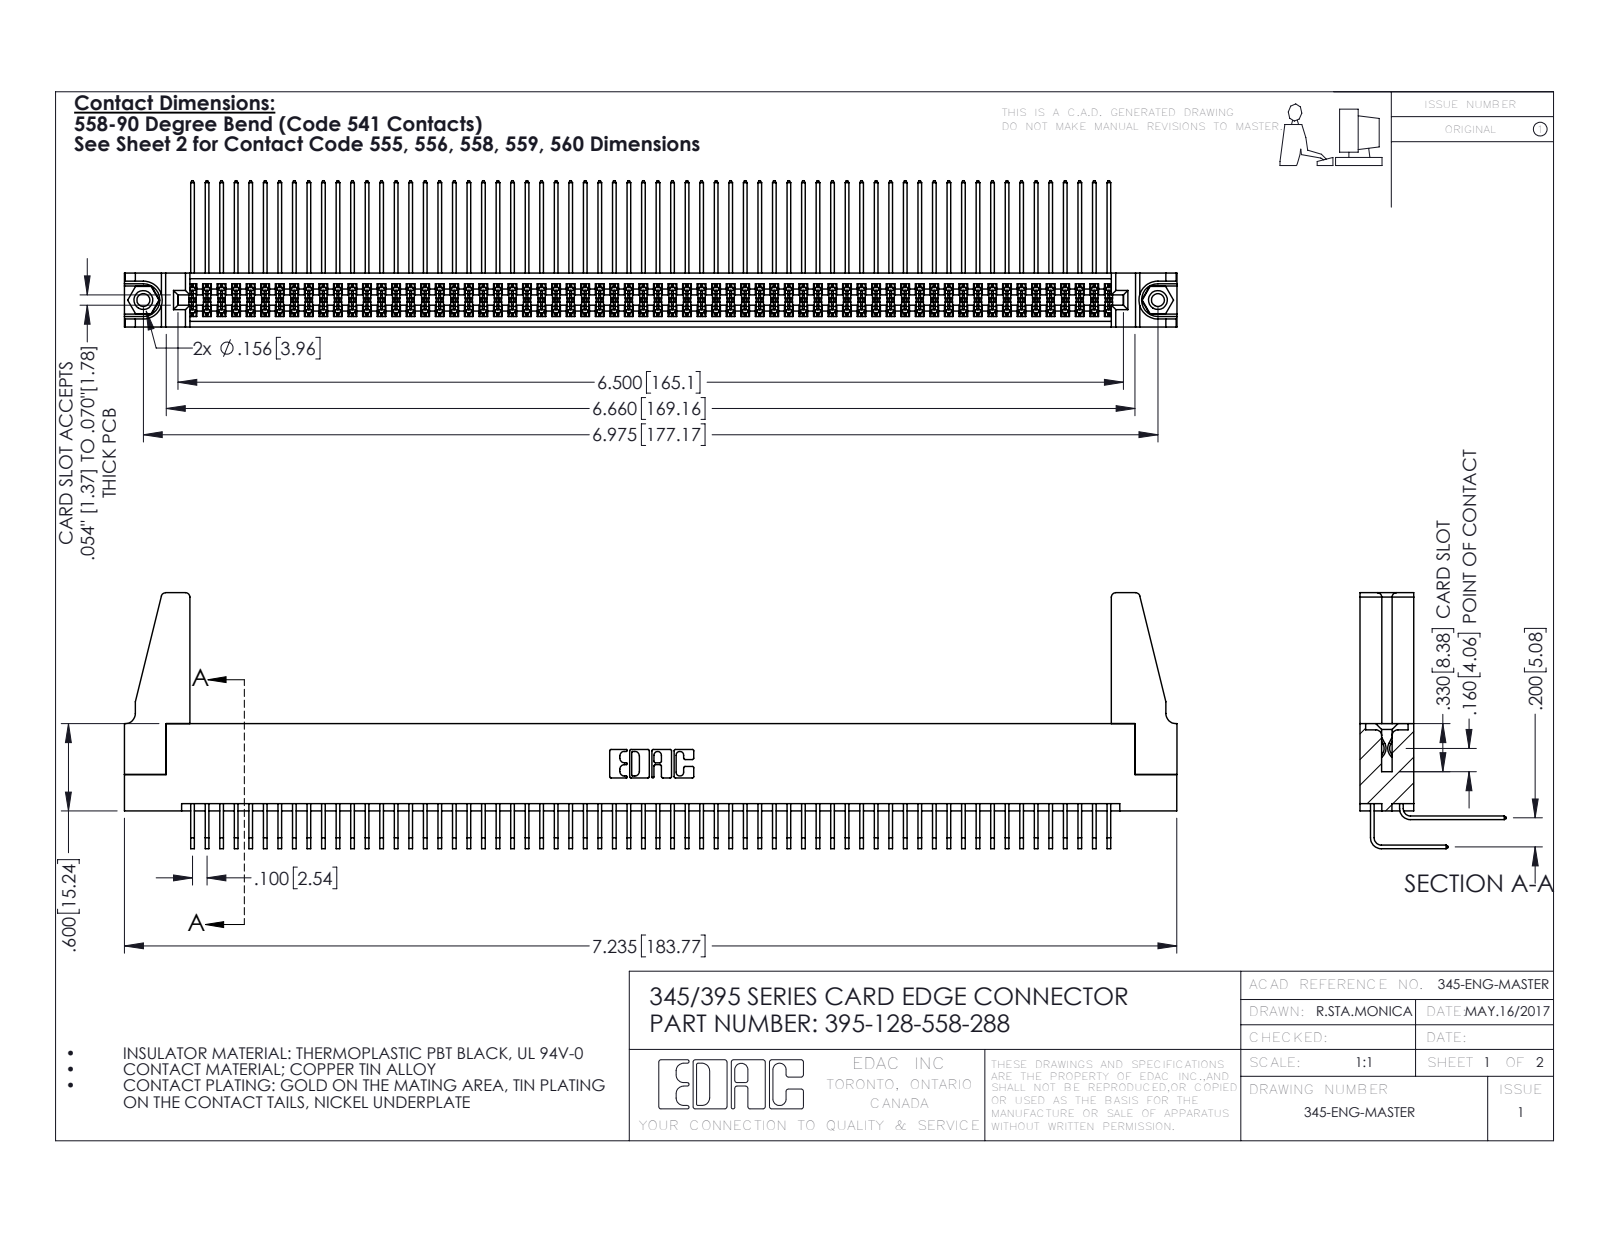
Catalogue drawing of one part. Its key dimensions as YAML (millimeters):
part_name: "345-250-001_345-250-001-102; 345-292-001_558 Tail - 2; 345-220-078_345-220-088; 345-292-001_558 559 Tail - 1 (+2 more)"
step_written_by: "SolidWorks 2016 (CONFIG_CONTROL_DESIGN)"
units: millimeters
bodies: {solids: 133, faces: 6906, planar: 4632, cylindrical: 2258, other: 16}
overall_size: [183.8, 44.7, 25.5]
volume: 22060
surface_area: 34810
round_holes:
  - {diameter: 2.3, count: 2}
  - {diameter: 3.2, count: 2}
  - {diameter: 4, count: 2}
  - {diameter: 1.6, count: 1}
round_bosses_or_shafts:
  - {diameter: 3.9, count: 2}
partial_cylinders:
  - {radius: 0.2, count: 193}
  - {radius: 0.3, count: 22}
  - {radius: 0.8, count: 8}
  - {radius: 0.2, count: 6}
  - {radius: 0.8, count: 6}
  - {radius: 0.7, count: 3}
  - {radius: 0.4, count: 2}
  - {radius: 0.5, count: 2}
face_to_face_distances: [1.8, 7.6, 5.1, 9.4, 2.5, 6.9, 0.6, 5.7, 0.6, 7.2]
hole_center_spacings: [6.9, 171.2, 177.2]
